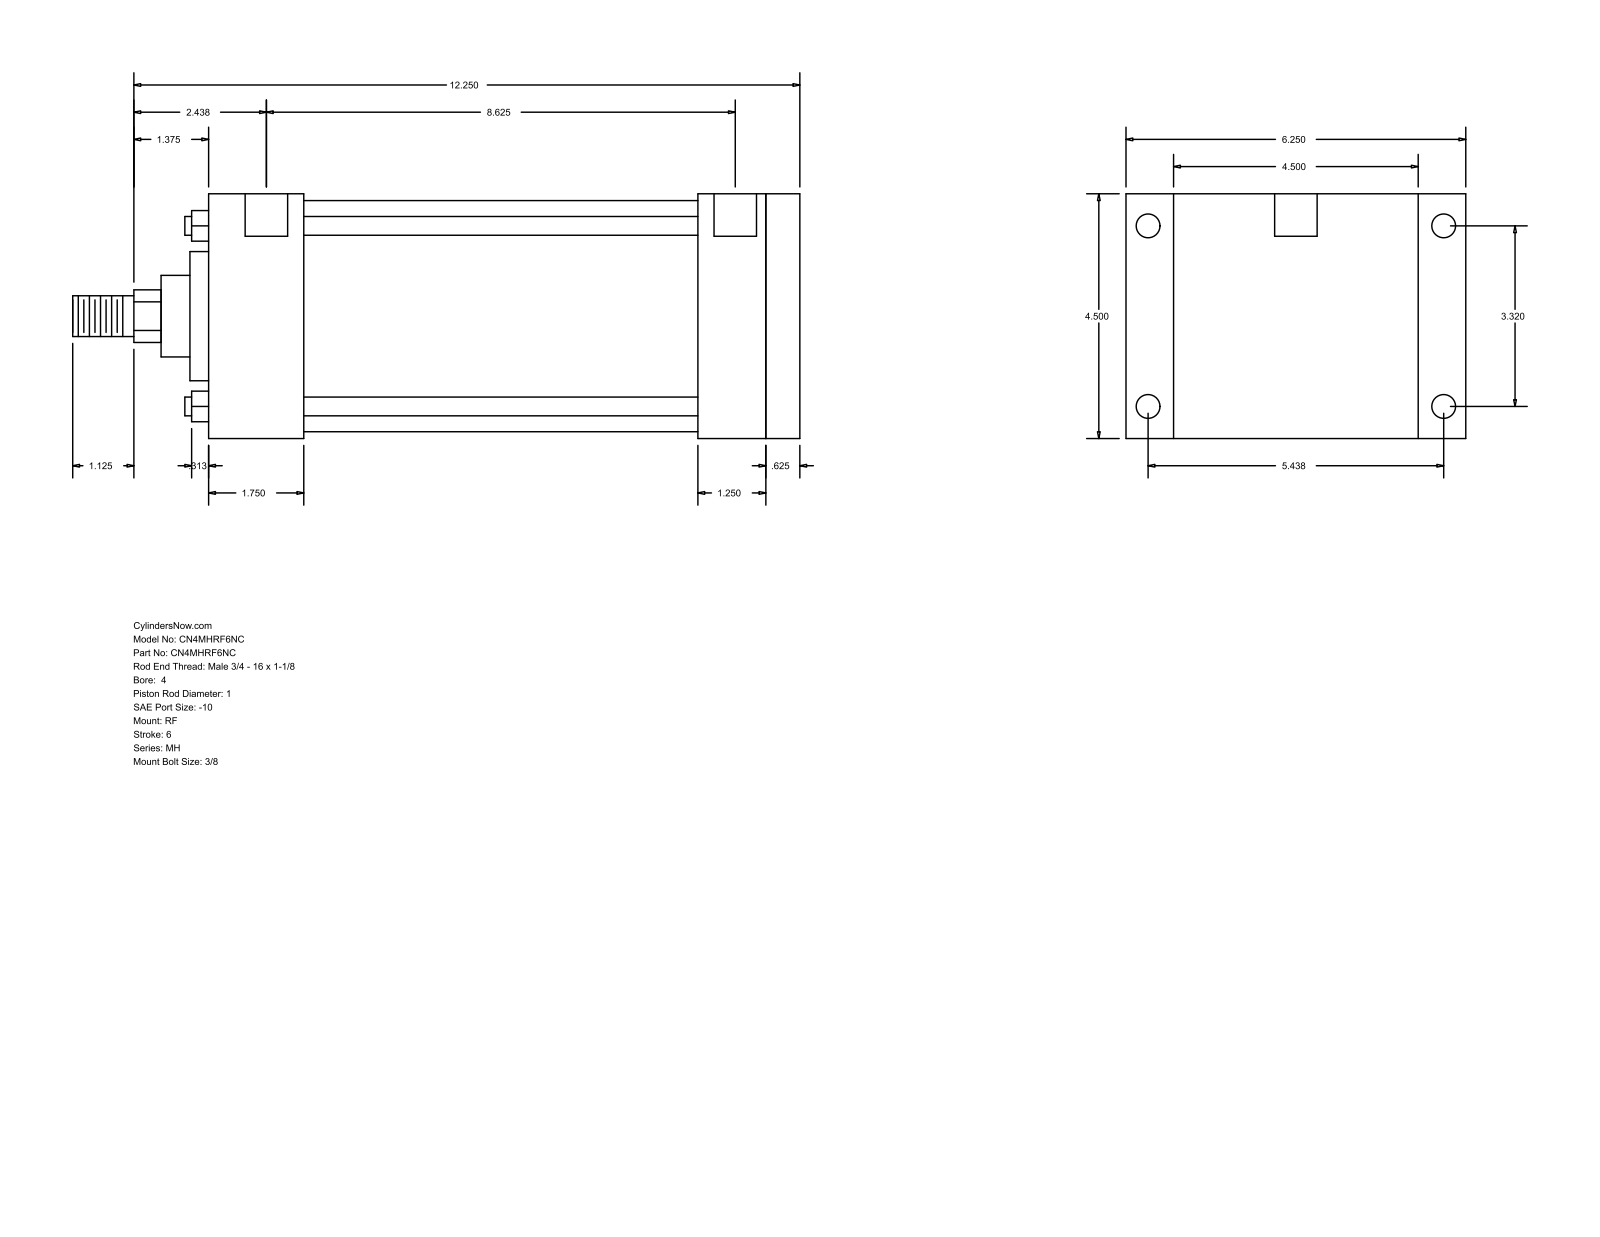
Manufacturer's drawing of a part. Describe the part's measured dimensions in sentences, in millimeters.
The part is named "MH_RF__0400_1". Its 3-D file was written by "GSSL Pune (CONFIG_CONTROL_DESIGN)". It is 0 solids with 94 faces: 65 planar, 29 cylindrical and 0 other. Overall it measures 339.73 by 158.75 by 114.3 millimeters. Round holes: 4 of diameter 8.73, 4 of diameter 11.13, 2 of diameter 19.84. Round bosses or shafts: 4 of diameter 8.76, 1 of diameter 107.95, 1 of diameter 60.33, 1 of diameter 38.1, 1 of diameter 25.4, 1 of diameter 19.05. Partial cylindrical surfaces (rounded edges, fillets, slot ends): 1 of radius 12.29. The main face-to-face distances are 114.3, 276.23, 260.35, 15.88, 47.63, 44.46, 215.89, 231.77, 228.6, 184.14. The hole center spacings are 1.58, 84.32, 138.12, 161.82, 220.66, 222.24, 219.08.
